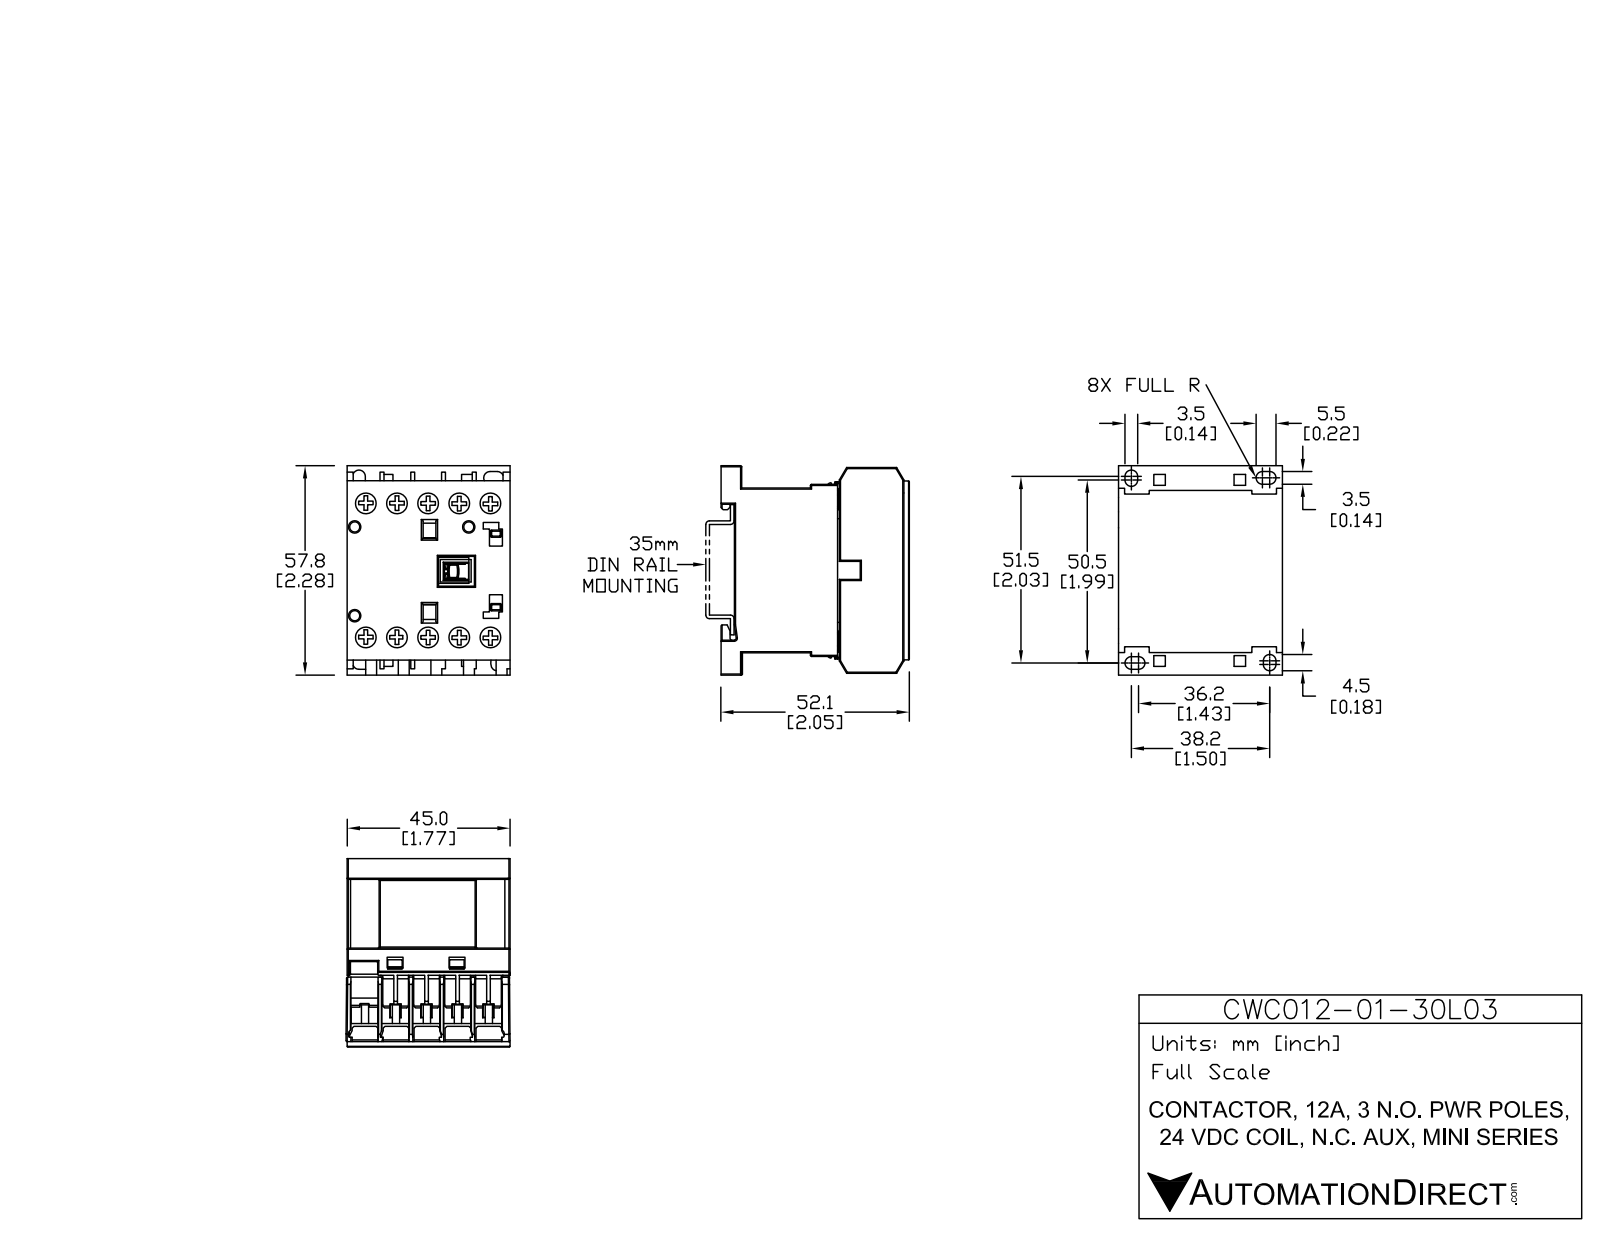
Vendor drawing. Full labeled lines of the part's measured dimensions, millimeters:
Part name (STEP PRODUCT): CWC12-01-30L03
STEP written by: SolidWorks 2013 (AUTOMOTIVE_DESIGN)
Units: millimetres
Bodies: 15 solids, 535 faces (445 planar, 90 cylindrical, 0 other)
Overall size (bounding box): 58.04 × 52.12 × 45.75
Volume: 97 133 mm³ · Surface area: 30 437 mm²
Round holes (diameter × count): ⌀6.2 ×10, ⌀2.8 ×3
Round bosses / shafts (diameter × count): ⌀5.9 ×10
Partial cylindrical surfaces — rounded edges, fillets, slot ends (radius × count): R0.3 ×20, R1.72 ×6, R1.73 ×2, R0.32 ×1, R0.42 ×1, R0.55 ×1
Main face-to-face distances: 8.25, 45.5, 1.25, 16.5, 9.5, 5.5, 17.75, 5.13, 10.63, 7
Hole centre spacings: 8.55, 37.94, 17.1, 40.72, 36.96, 25.65, 44.99, 6.91
